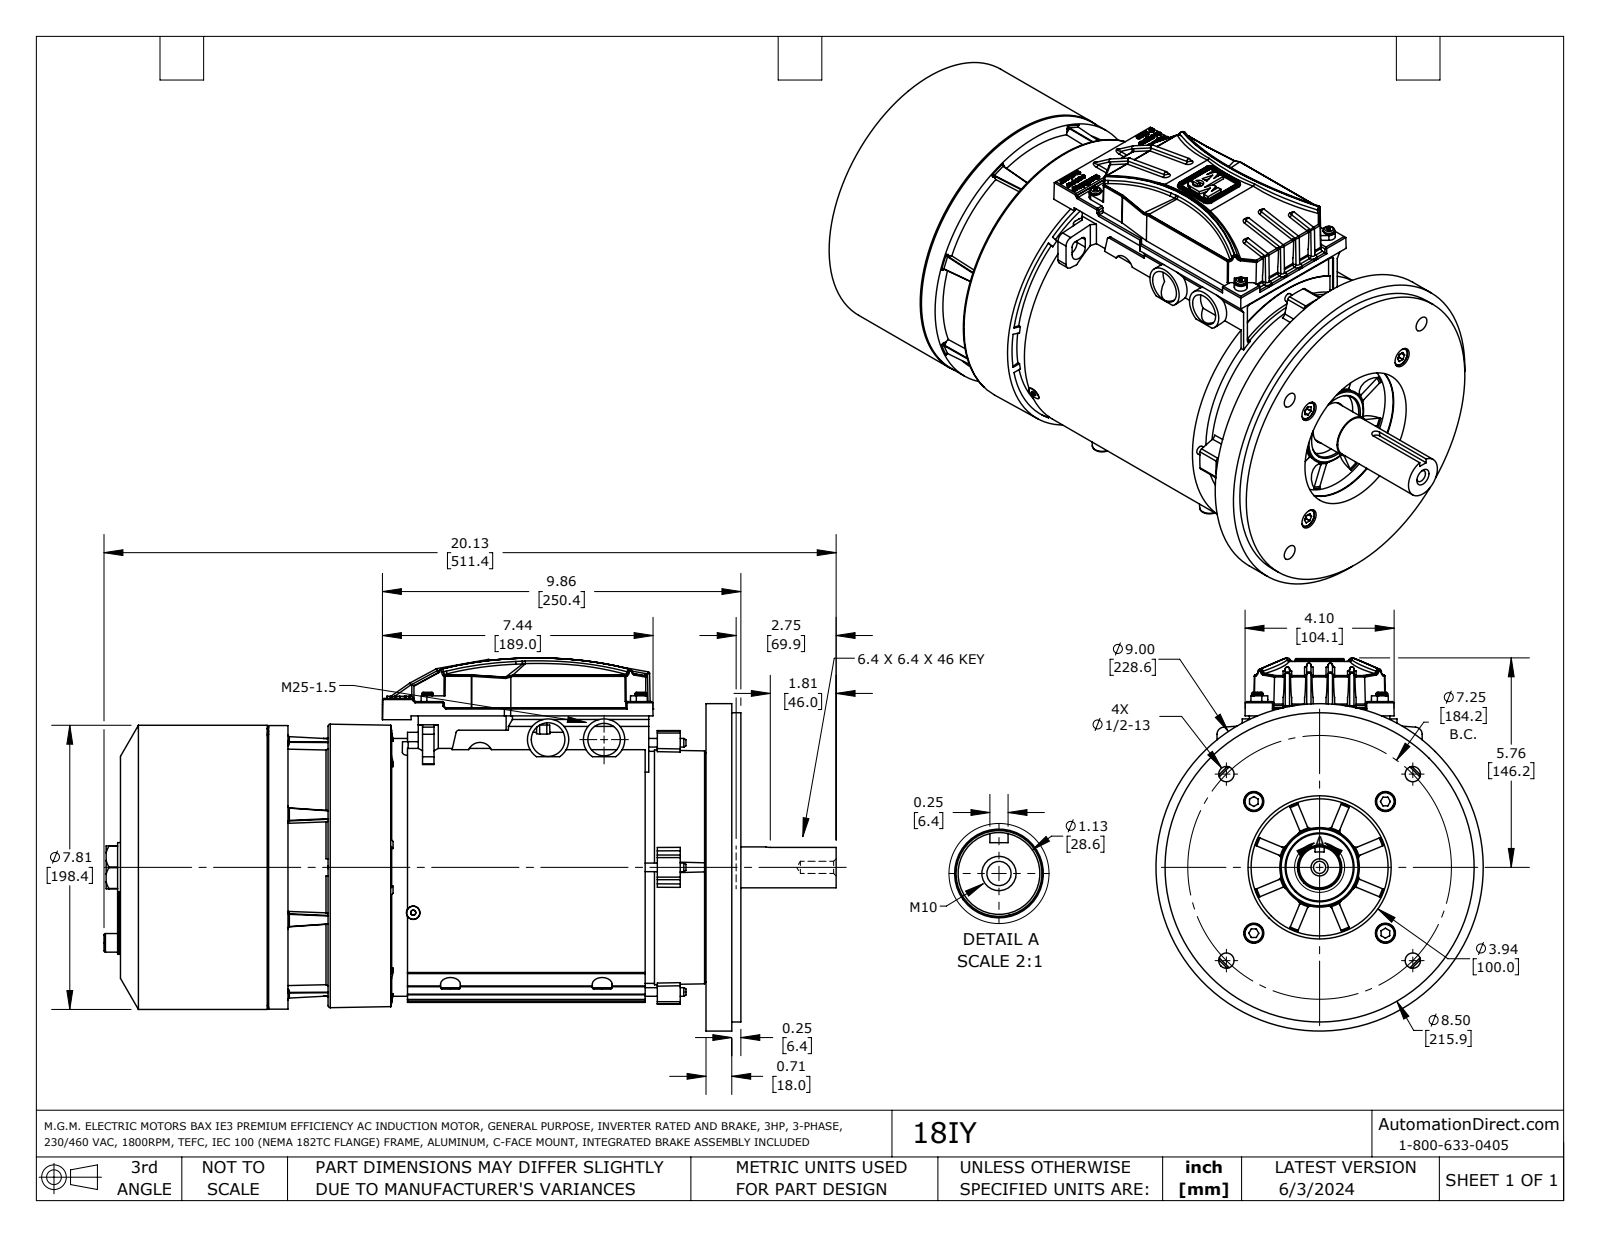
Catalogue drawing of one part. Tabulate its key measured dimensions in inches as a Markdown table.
| quantity | value |
| --- | --- |
| part name | 18IY |
| STEP written by | SolidWorks 2021 (AUTOMOTIVE_DESIGN) |
| units | inches |
| bodies | 15 solids, 3150 faces (1253 planar, 723 cylindrical, 1174 other) |
| overall size | 20.134 × 10.258 × 9 |
| volume | 704.9 in³ |
| surface area | 1 207 in² |
| round holes (diameter × count) | 0.13 × 6, 0.15 × 4, 0.177 × 4, 0.197 × 4, 0.268 × 4, 0.315 × 4, 0.354 × 4, 0.422 × 4, 0.551 × 4, 0.098 × 3, 0.276 × 3, 0.118 × 2 |
| round bosses / shafts (diameter × count) | 0.315 × 8, 0.138 × 6, 0.522 × 4, 0.236 × 4, 0.276 × 3, 1.138 × 2, 9 × 1, 8.5 × 1 |
| partial cylindrical surfaces (radius × count) | 0.008 × 56, 0.059 × 49, 0.079 × 30, 0.004 × 24, 0.039 × 24, 0.02 × 22, 0.033 × 16, 0.197 × 12 |
| main face-to-face distances | 12.986, 0.644, 12.343, 0.315, 0.039, 0.959, 12.028, 2.376, 1.732, 1.417 |
| hole center spacings | 2.426, 2.704, 4.437, 5.539, 6.514, 3.425, 5.127, 1.066 |
